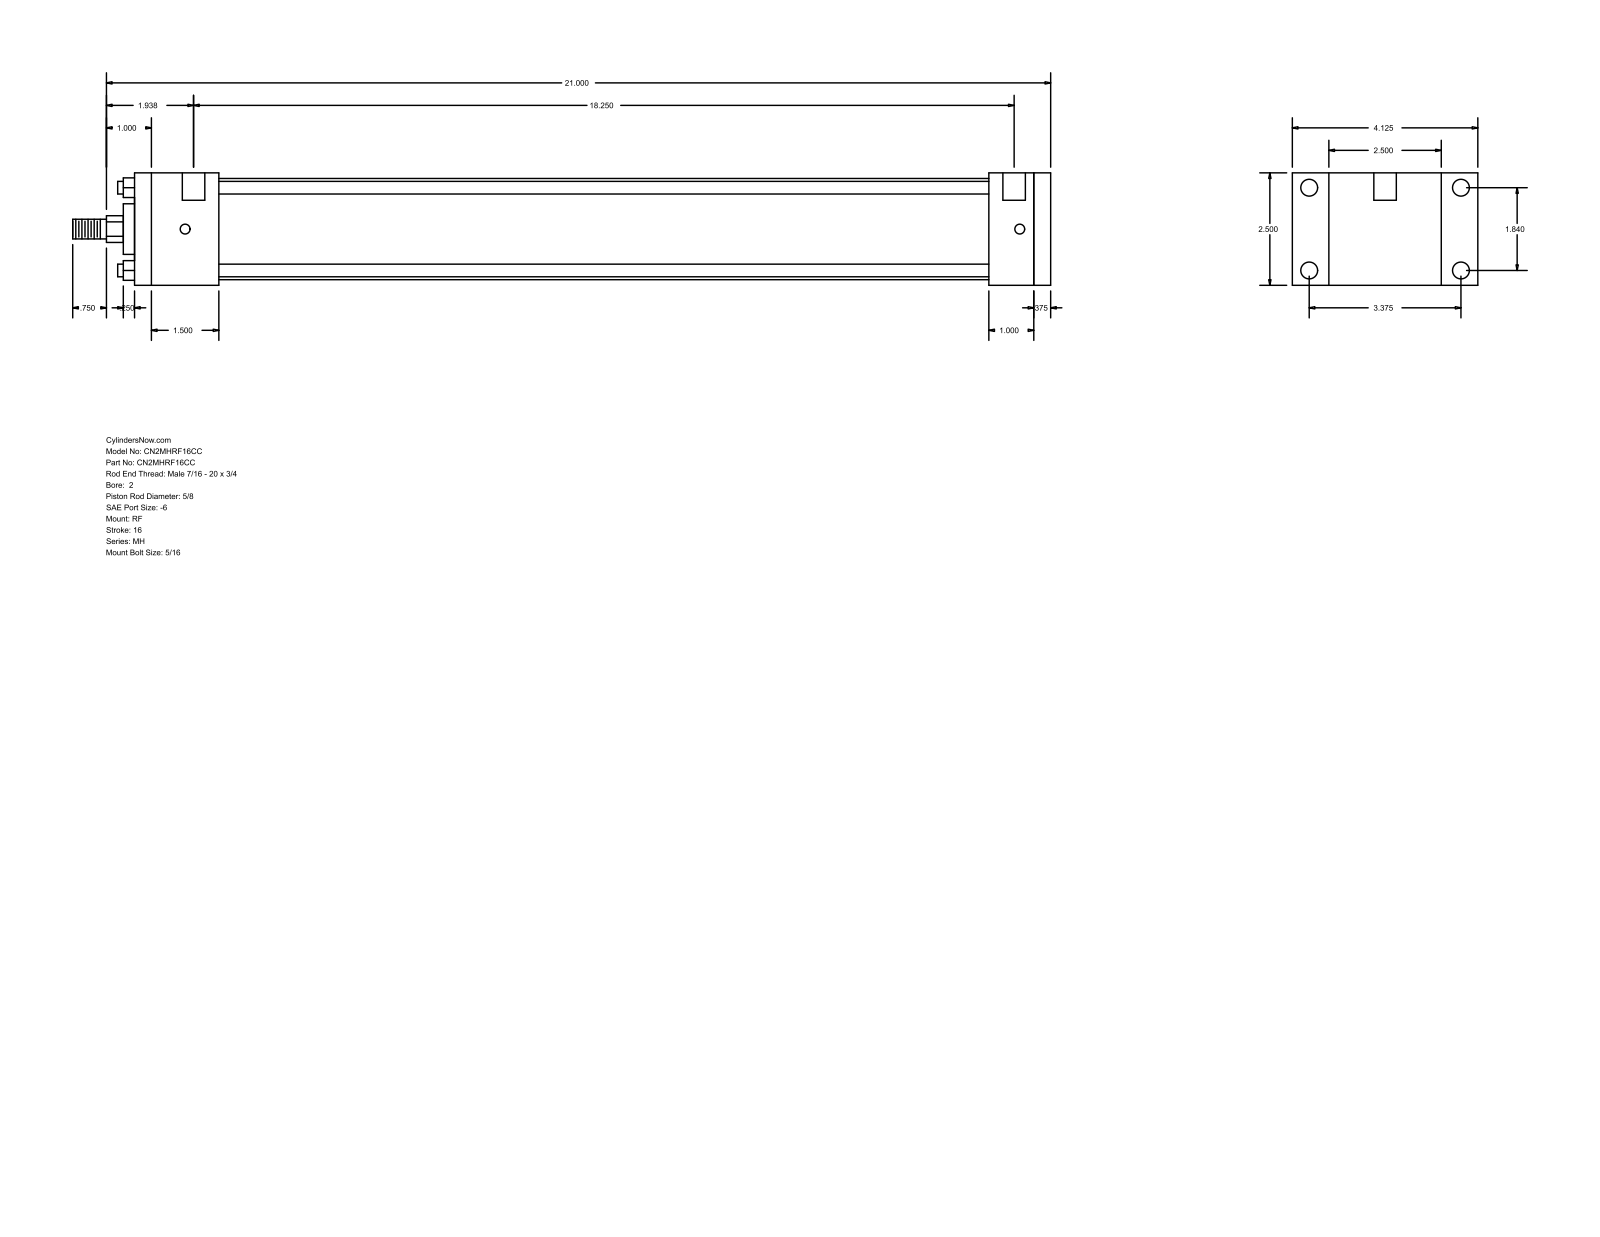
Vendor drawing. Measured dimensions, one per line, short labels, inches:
name: MH_RF__0200_0.625
written by: GSSL Pune (CONFIG_CONTROL_DESIGN)
unit: in
bodies: 0 solids, 92 faces (64 planar, 28 cylindrical, 0 other)
size: 21.75 × 4.125 × 2.5
holes: 4× ⌀0.219, 4× ⌀0.375, 2× ⌀0.5
bosses: 4× ⌀0.281, 1× ⌀2.25, 1× ⌀1.125, 1× ⌀0.625, 1× ⌀0.437
rounds: 1× R0.297
face distances: 2.5, 20.375, 20, 0.375, 1, 1.875, 19, 17.125, 18.125, 18.5
hole spacings: 1.84, 3.375, 3.844, 18.563, 0.125, 0.187, 18.25, 18.375
